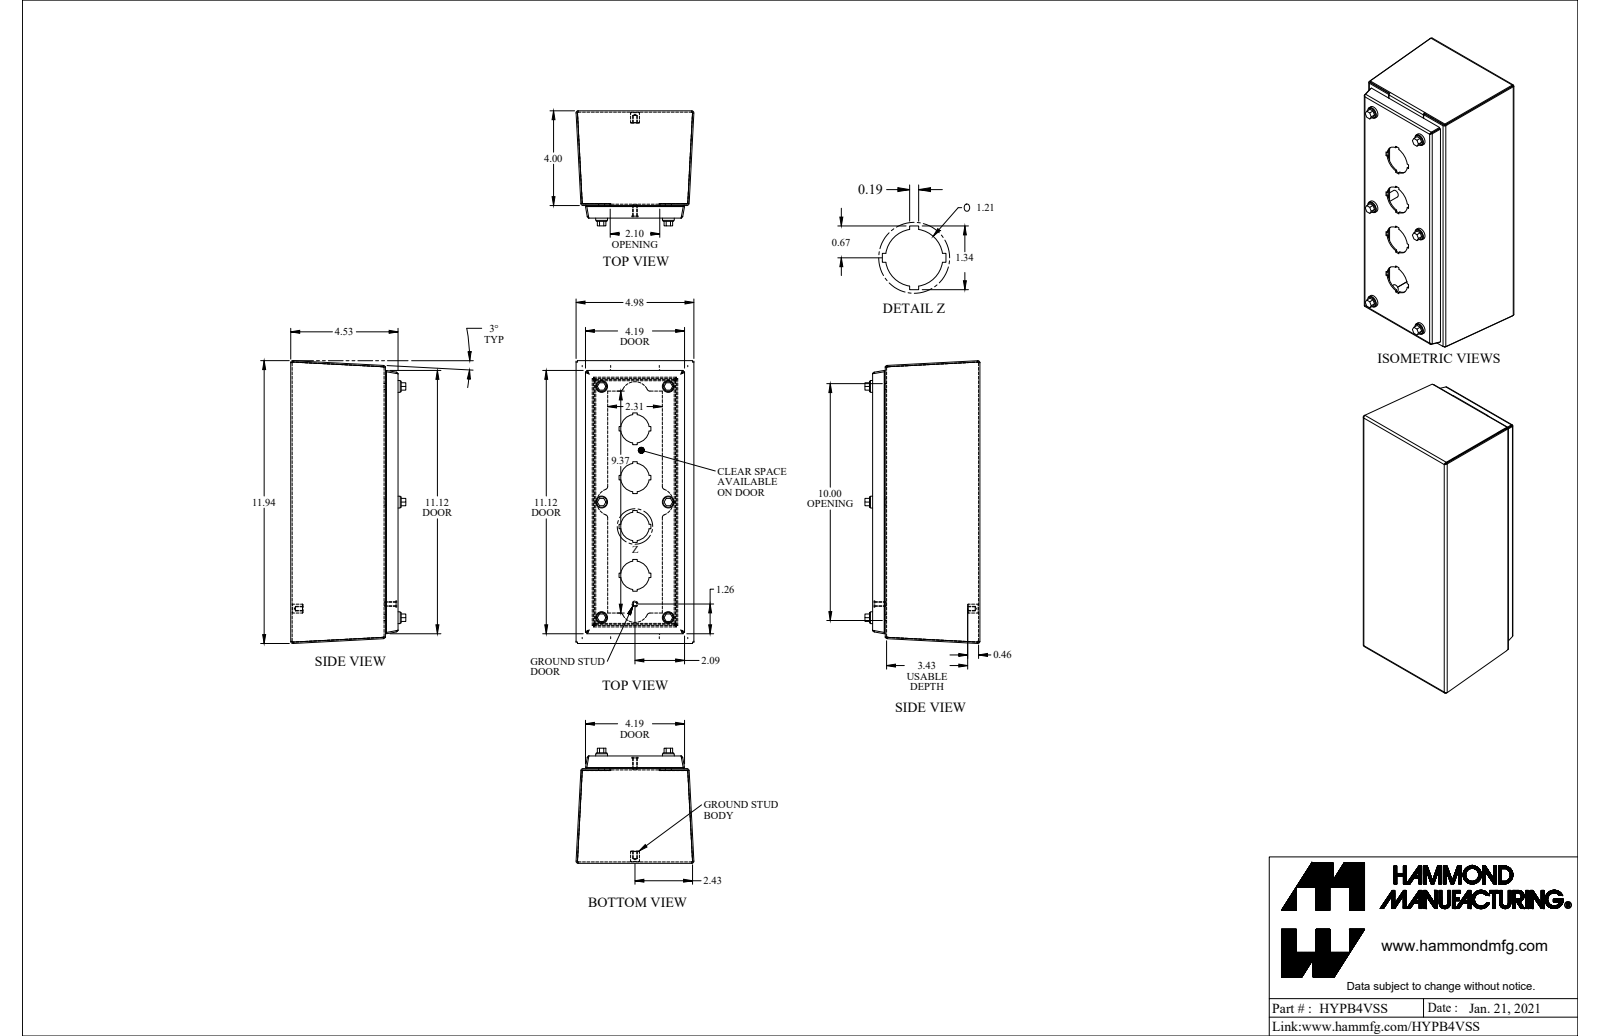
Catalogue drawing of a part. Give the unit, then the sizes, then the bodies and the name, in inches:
Units: inches
Overall size (bounding box): 11.942 × 4.976 × 4.859
Round holes (diameter × count): ⌀0.065 ×6, ⌀0.235 ×6, ⌀0.239 ×6, ⌀0.24 ×6, ⌀0.25 ×6, ⌀0.253 ×6, ⌀0.4 ×4, ⌀1.21 ×4, ⌀0.156 ×1
Round bosses / shafts (diameter × count): ⌀0.375 ×7, ⌀0.19 ×7, ⌀0.5 ×6, ⌀0.45 ×6, ⌀0.406 ×6, ⌀0.315 ×6, ⌀0.25 ×1
Partial cylindrical surfaces — rounded edges, fillets, slot ends (radius × count): R0.029 ×16, R0.086 ×16, R0.125 ×8, R0.076 ×6, R0.055 ×4, R0.5 ×4, R0.575 ×4
Main face-to-face distances: 0.057, 4.418, 3.943, 4.475, 0.475, 0.057, 4.532, 4.475, 4, 0.532
Hole centre spacings: 10.165, 2.819, 4.883, 5.638, 9.766, 4.883, 9.766, 2.278
Volume: 21.11 in³ · Surface area: 678.9 in²
Bodies: 30 solids, 597 faces (394 planar, 178 cylindrical, 25 other)
Part name (STEP PRODUCT): HYPB4VSS
STEP written by: SolidWorks 2021 (AUTOMOTIVE_DESIGN)
